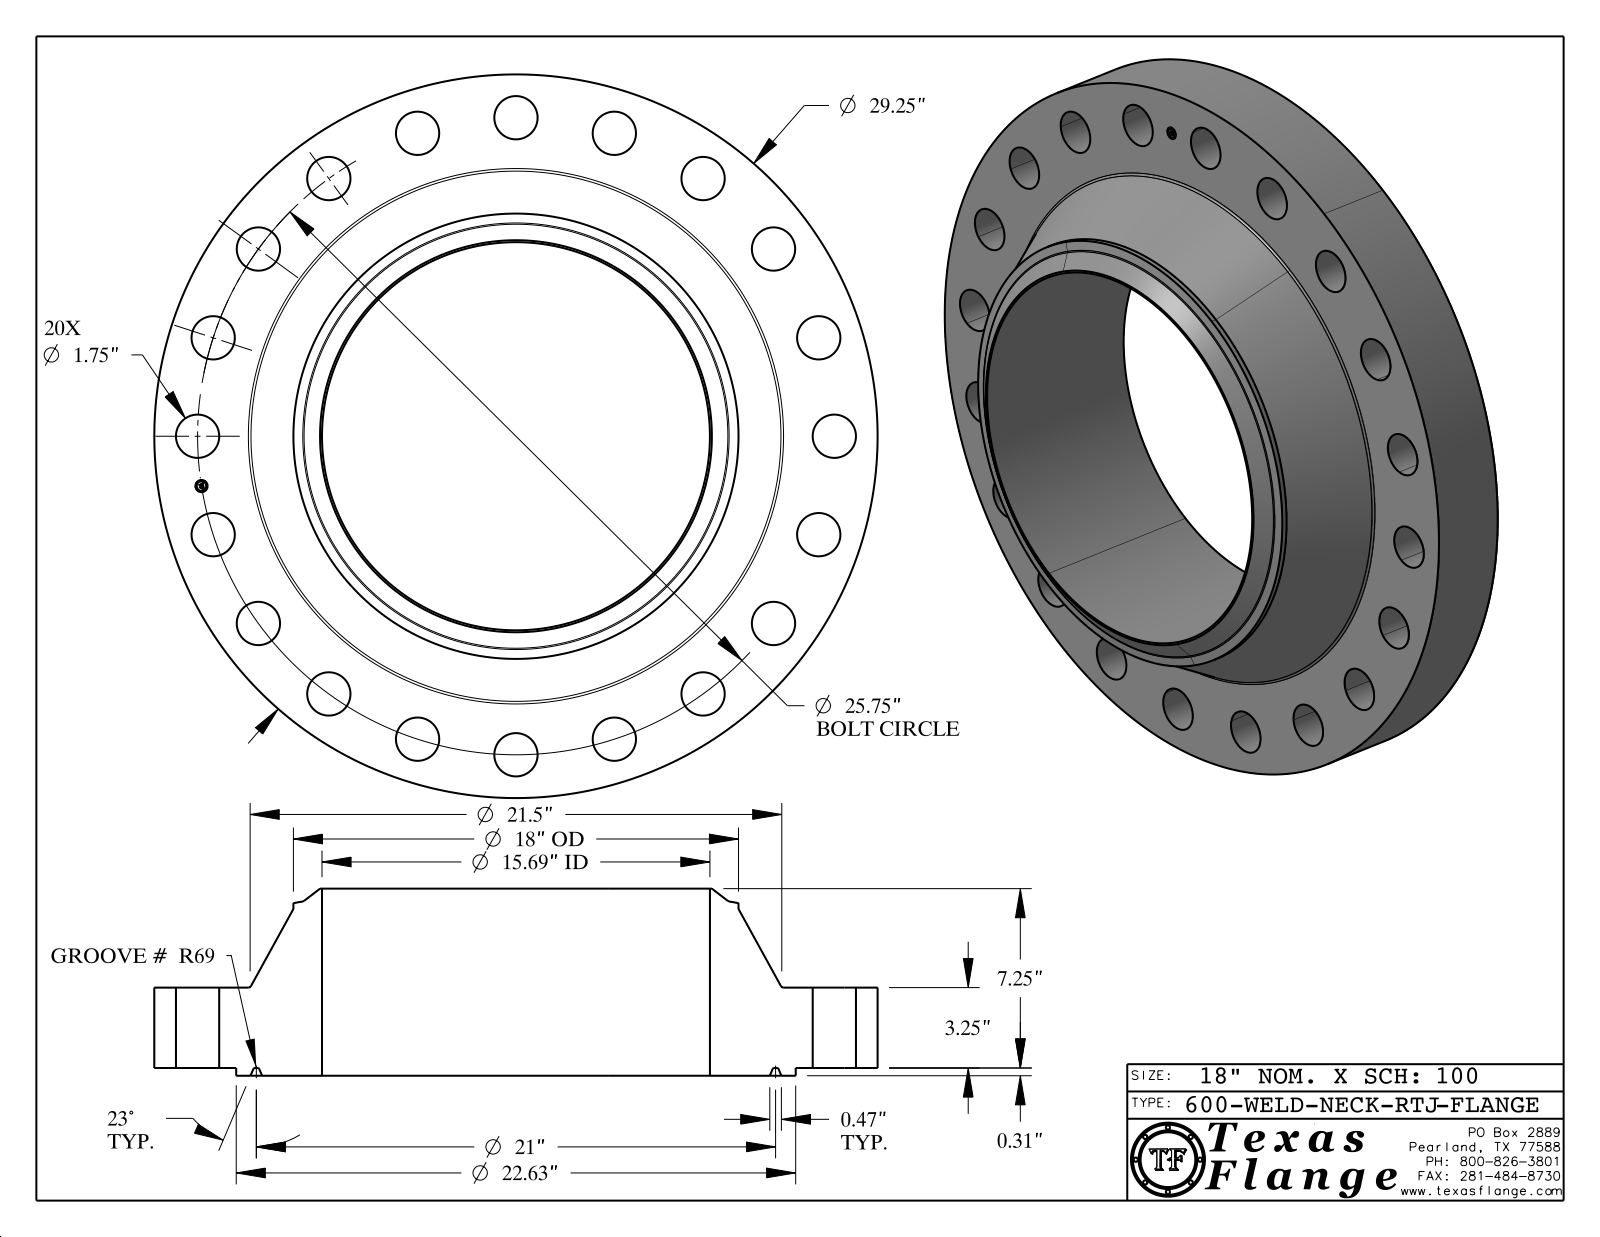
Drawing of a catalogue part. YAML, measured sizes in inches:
part_name: "600-WELD-NECK-RTJ"
step_written_by: "CATIA V5 STEP AP214 (AUTOMOTIVE_DESIGN)"
units: inches
bodies: {solids: 1, faces: 457, planar: 371, cylindrical: 68, other: 18}
overall_size: [29.25, 29.25, 7.563]
volume: 1848
surface_area: 2077
round_holes:
  - {diameter: 1.75, count: 20}
  - {diameter: 0.495, count: 1}
  - {diameter: 15.688, count: 1}
round_bosses_or_shafts:
  - {diameter: 0.03, count: 8}
  - {diameter: 29.25, count: 1}
  - {diameter: 22.625, count: 1}
  - {diameter: 18, count: 1}
  - {diameter: 0.39, count: 1}
face_to_face_distances: [3.25, 0.313, 3.563, 7.563, 7.25, 4, 0.015, 3.548, 3.235, 4.015]
hole_center_spacings: [12.875, 24.49, 25.433, 7.957, 11.691, 4.028, 15.135, 18.208]
